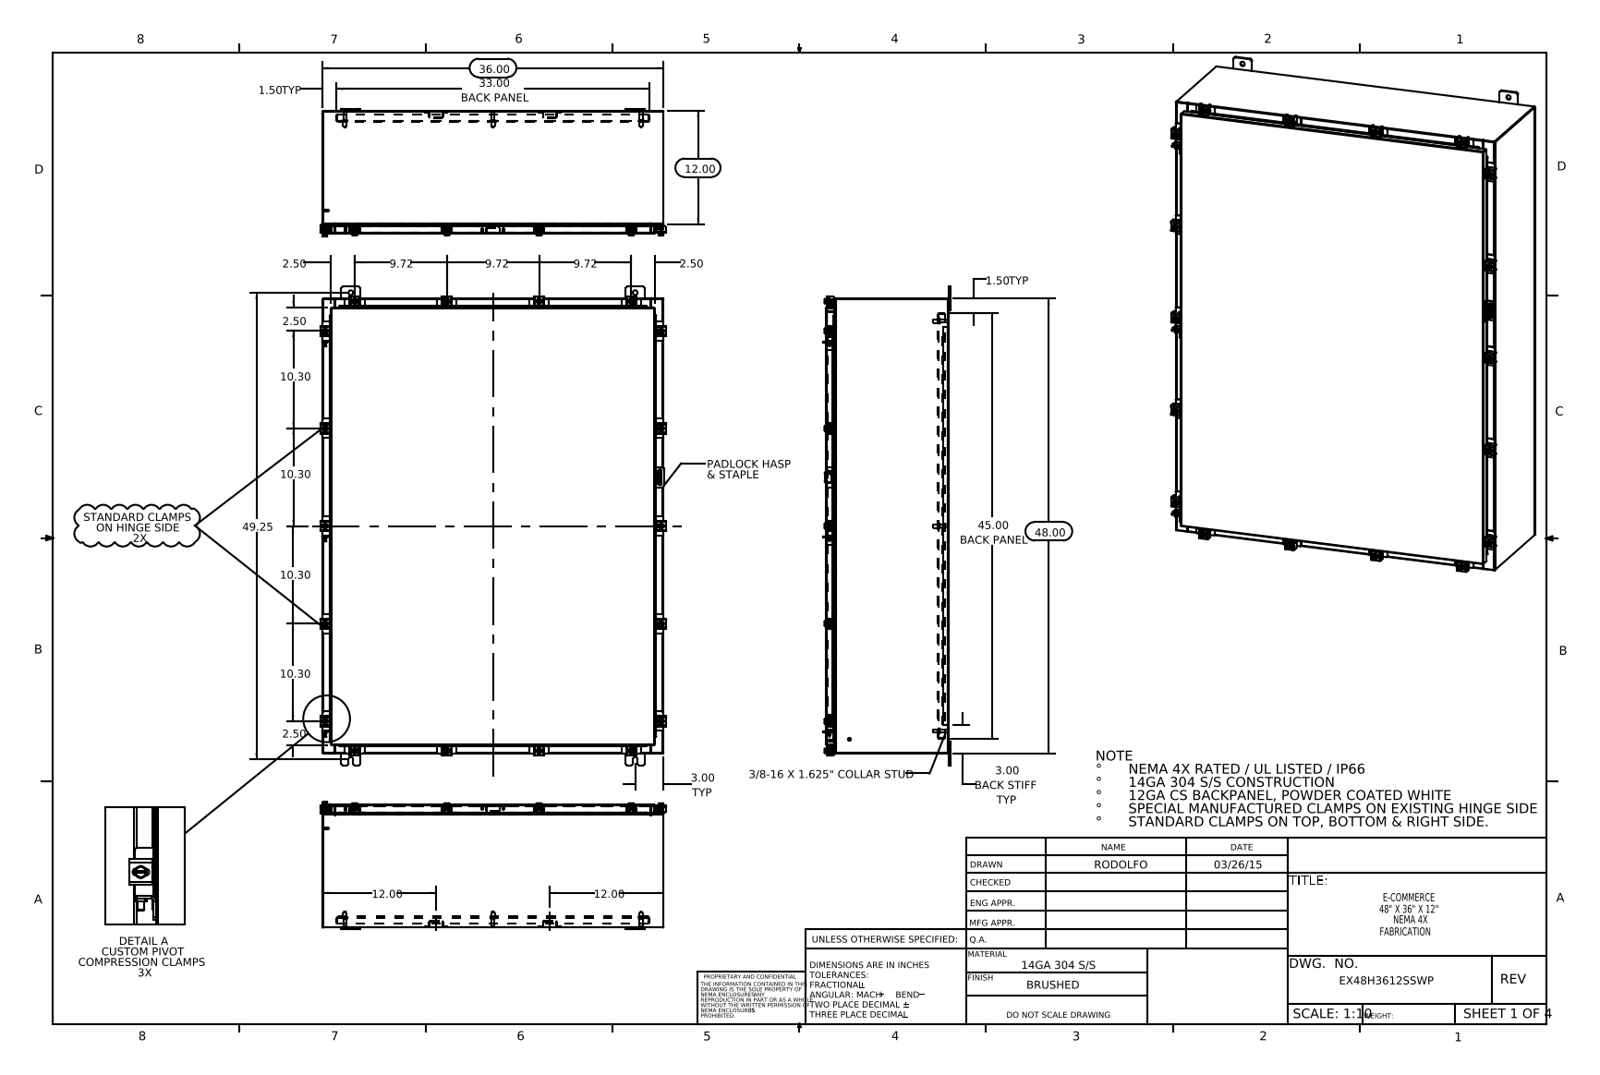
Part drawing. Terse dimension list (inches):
name: 30X10 Clamp Bracket2; EX48H3612SSWP Standard Clamps; EX48H3612SSWP Cover; N-WMT04X30402202210-00 22104005_DEFAULT (+8 more)
written by: SolidWorks 2014 (CONFIG_CONTROL_DESIGN)
unit: in
bodies: 130 solids, 3206 faces (1681 planar, 1223 cylindrical, 302 other)
size: 50.5 × 36.421 × 13.453
volume: 649.1 in³; area: 16 147 in²
holes: 18× ⌀0.213, 18× ⌀0.26, 12× ⌀0.5, 7× ⌀0.25, 1× ⌀0.125
bosses: 18× ⌀0.5, 18× ⌀0.25, 13× ⌀0.399, 8× ⌀0.625, 8× ⌀0.375, 8× ⌀0.33, 6× ⌀0.157, 6× ⌀0.14
rounds: 70× R0.06, 38× R0.013, 36× R0.141, 34× R0.088, 33× R0.09, 31× R0.12, 29× R0.05, 28× R0.145
face distances: 0.075, 12.9, 12.826, 12.975, 0.104, 1, 1.075, 11.826, 11.9, 1.179
hole spacings: 1.969, 2.347, 4.44, 13.972, 14.728, 16.126, 16.624, 17.756
